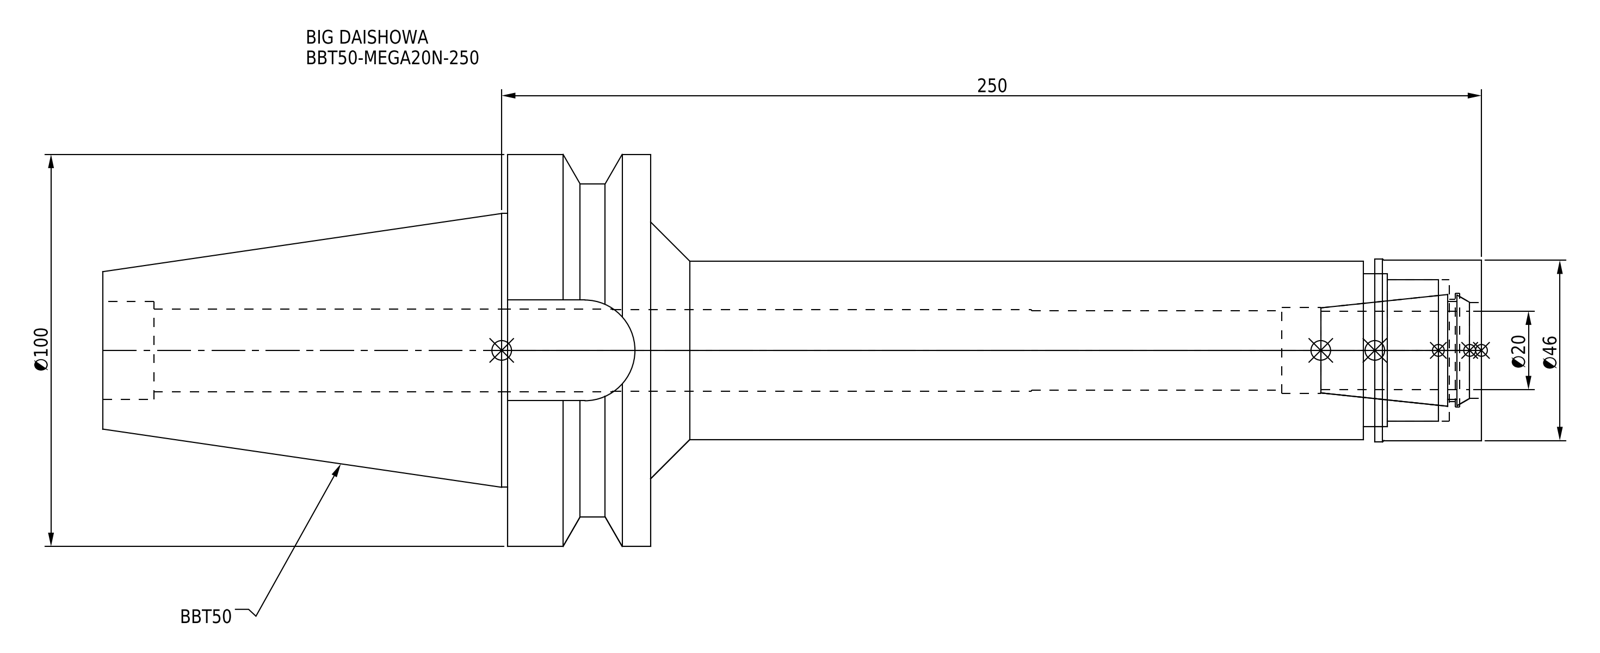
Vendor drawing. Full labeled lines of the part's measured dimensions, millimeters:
Part name (STEP PRODUCT): BBT50MN20250-200_ASM.stp; BBT50-MEGA20N-250_1.stp; BBT50-MEGA20N-250-200.stp; MGN20_1.stp (+3 more)
STEP written by: SolidWorks 2019 (CONFIG_CONTROL_DESIGN)
Units: millimetres
Bodies: 2 solids, 79 faces (23 planar, 42 cylindrical, 14 other)
Overall size (bounding box): 351.8 × 100 × 100
Volume: 721 383 mm³ · Surface area: 104 319 mm²
Round holes (diameter × count): ⌀20.3 ×1, ⌀20.8 ×1, ⌀21.2 ×1, ⌀22 ×1, ⌀24.5 ×1, ⌀25 ×1, ⌀26 ×1, ⌀29 ×1, ⌀36 ×1, ⌀39 ×1
Round bosses / shafts (diameter × count): ⌀100 ×1, ⌀85 ×1, ⌀69.85 ×1, ⌀46.7 ×1, ⌀46 ×1, ⌀45.5 ×1
Partial cylindrical surfaces — rounded edges, fillets, slot ends (radius × count): R12.85 ×1
Main face-to-face distances: 36.5, 212, 248.5, 351.8, 139.8, 103.3, 70.8, 27.2, 184.8, 221.3
